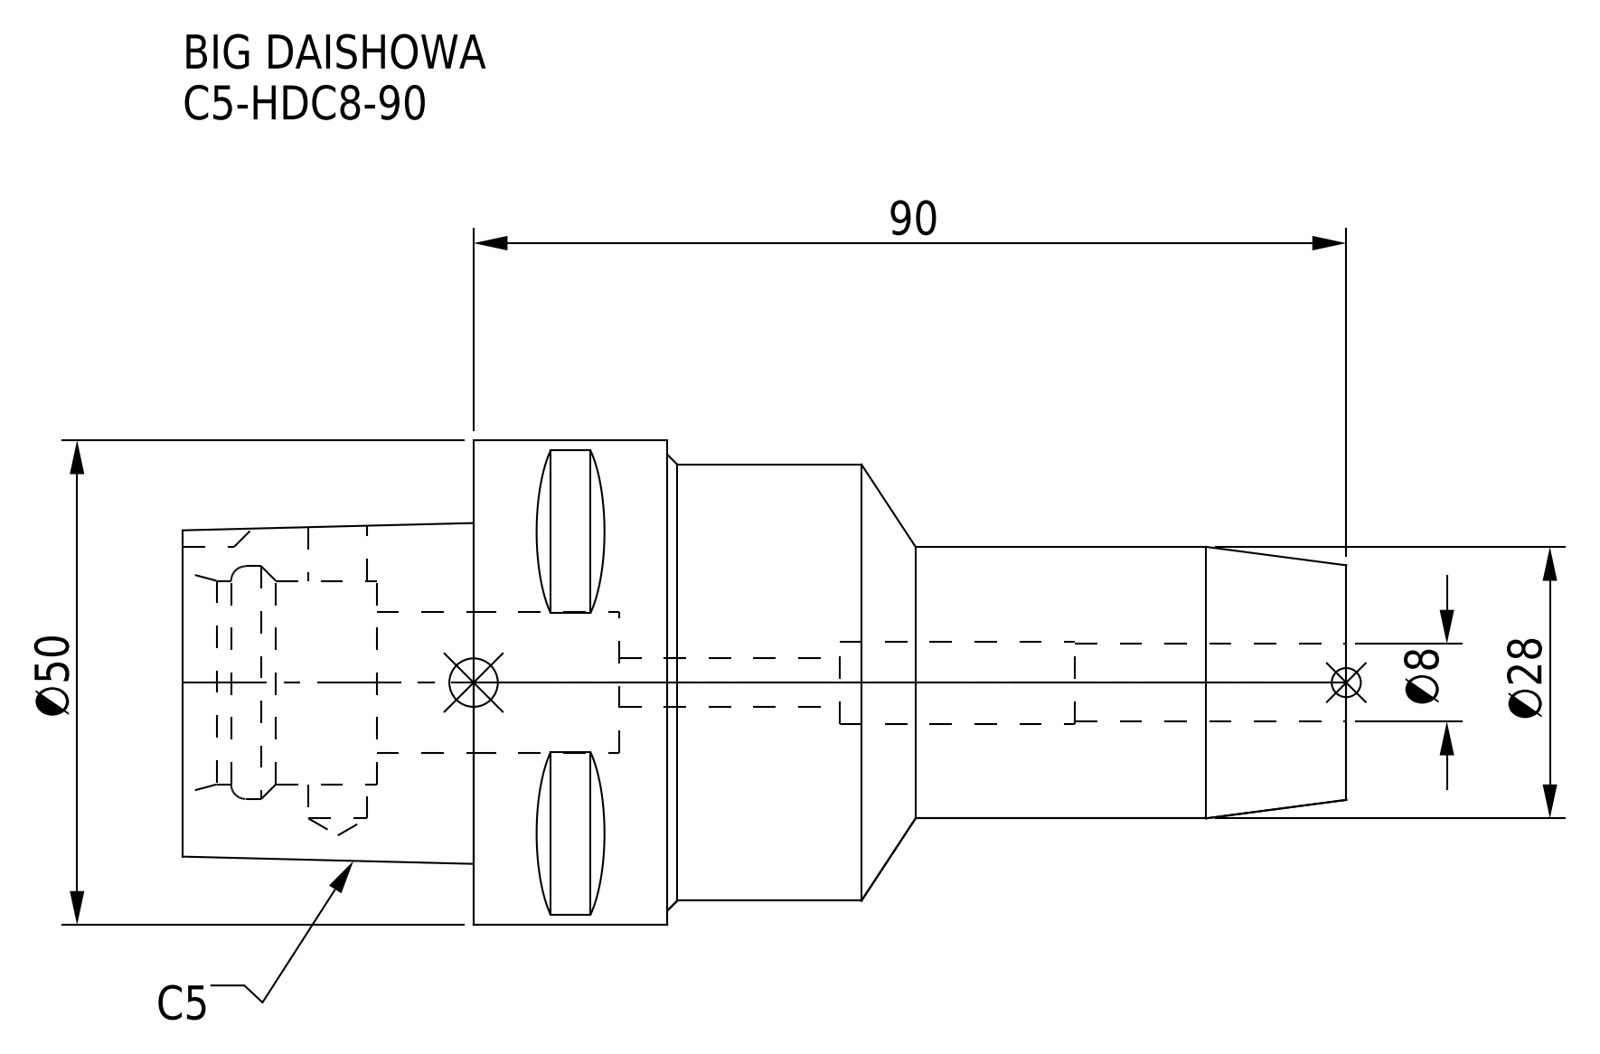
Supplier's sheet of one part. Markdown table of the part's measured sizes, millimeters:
| quantity | value |
| --- | --- |
| part name | C5-HDC8-90 |
| STEP written by | CREO PARAMETRIC BY PTC INC, 2016380 (AUTOMOTIVE_DESIGN) |
| units | millimeters |
| bodies | 1 solid, 71 faces (30 planar, 25 cylindrical, 16 other) |
| overall size | 120 × 50 × 50 |
| volume | 114 788 mm³ |
| surface area | 21 405 mm² |
| round holes (diameter × count) | 5 × 1, 6.1 × 1, 8 × 1, 8.5 × 1, 14.5 × 1, 21 × 1, 24 × 1 |
| round bosses / shafts (diameter × count) | 50 × 1, 45 × 1, 28 × 1 |
| partial cylindrical surfaces (radius × count) | 4 × 1 |
| main face-to-face distances | 30, 20, 90, 120, 70, 50, 44, 100, 10, 19.18 |
